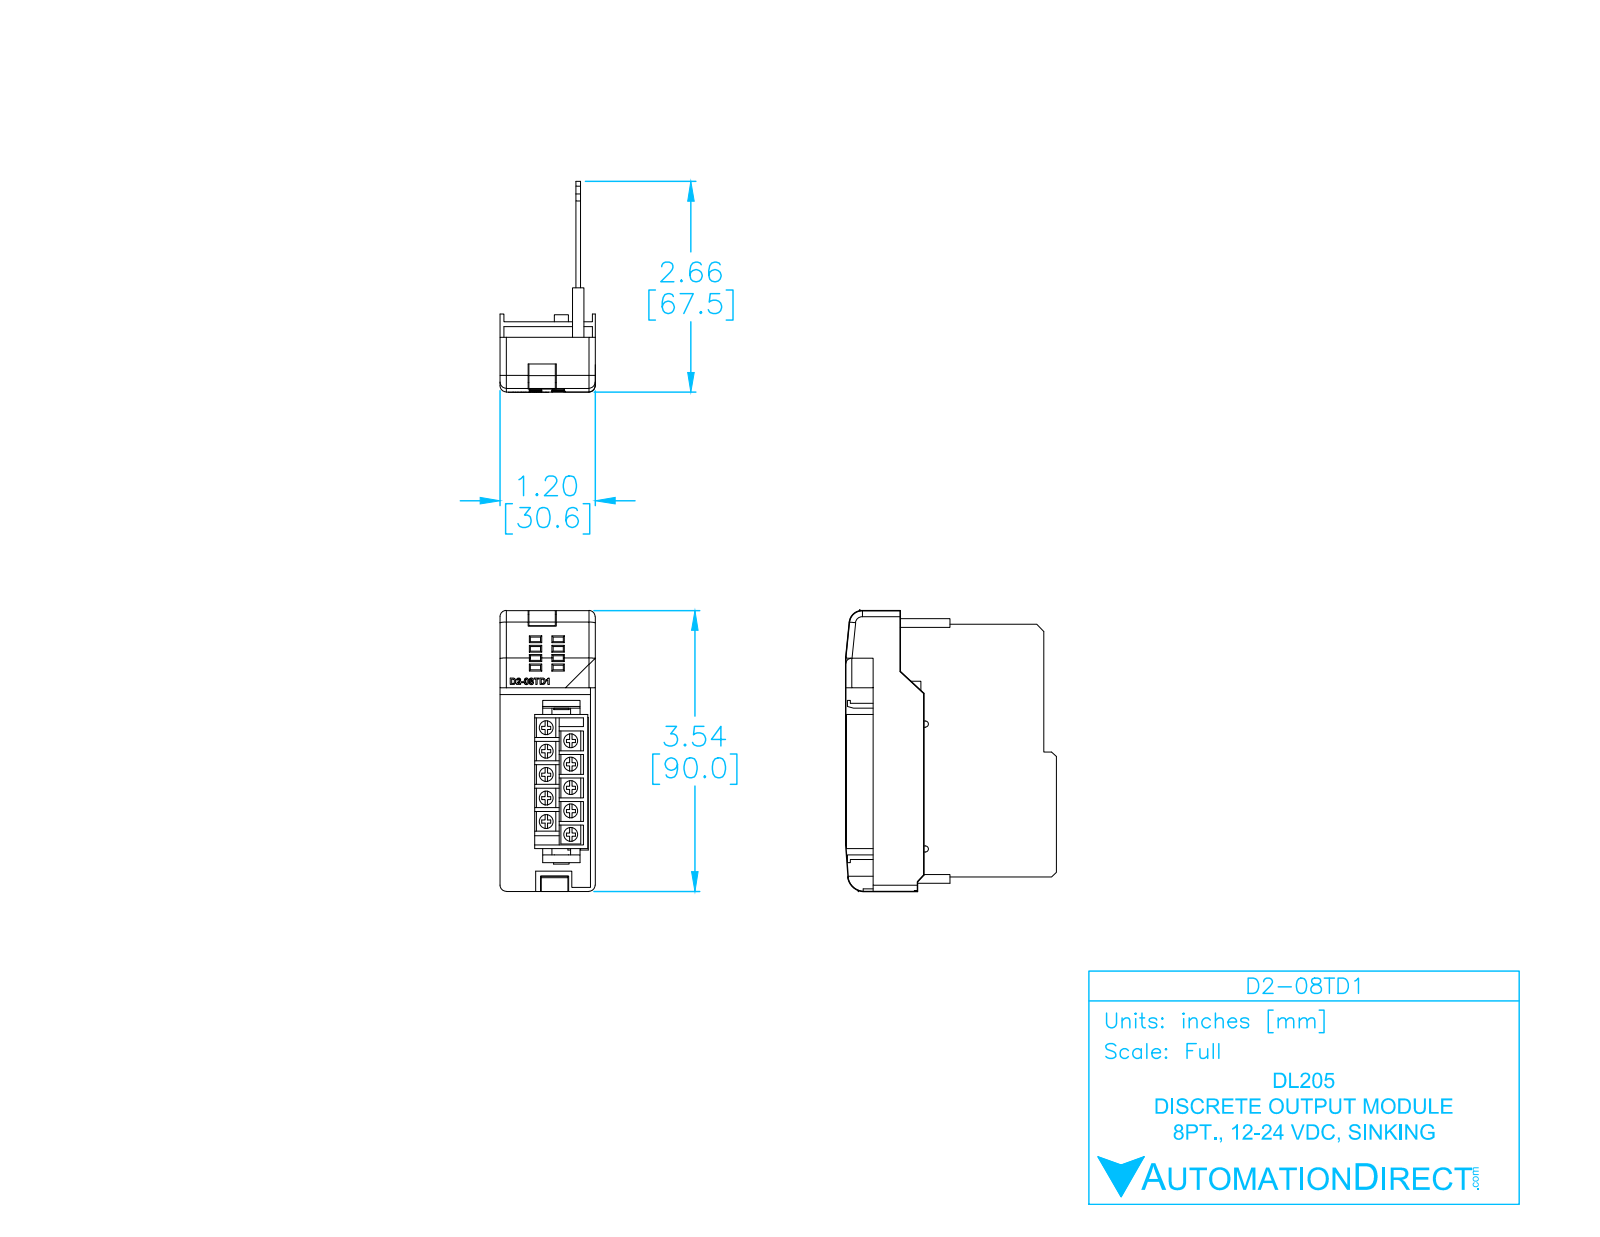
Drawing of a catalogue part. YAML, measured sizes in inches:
part_name: "D2-08TD1_ModuleCase_light_NEW"
step_written_by: "SolidWorks 2009 (AUTOMOTIVE_DESIGN)"
units: inches
bodies: {solids: 6, faces: 578, planar: 400, cylindrical: 75, other: 103}
overall_size: [3.543, 2.66, 1.203]
volume: 1.548
surface_area: 44.22
round_bosses_or_shafts:
  - {diameter: 0.177, count: 10}
partial_cylinders:
  - {radius: 0.014, count: 16}
  - {radius: 0.079, count: 9}
  - {radius: 0.01, count: 2}
  - {radius: 0.039, count: 2}
  - {radius: 0.049, count: 2}
  - {radius: 0.162, count: 1}
  - {radius: 0.212, count: 1}
face_to_face_distances: [0.059, 0.186, 0.245, 0.093, 0.152, 0.093, 0.127, 0.033, 0.32, 0.956]
